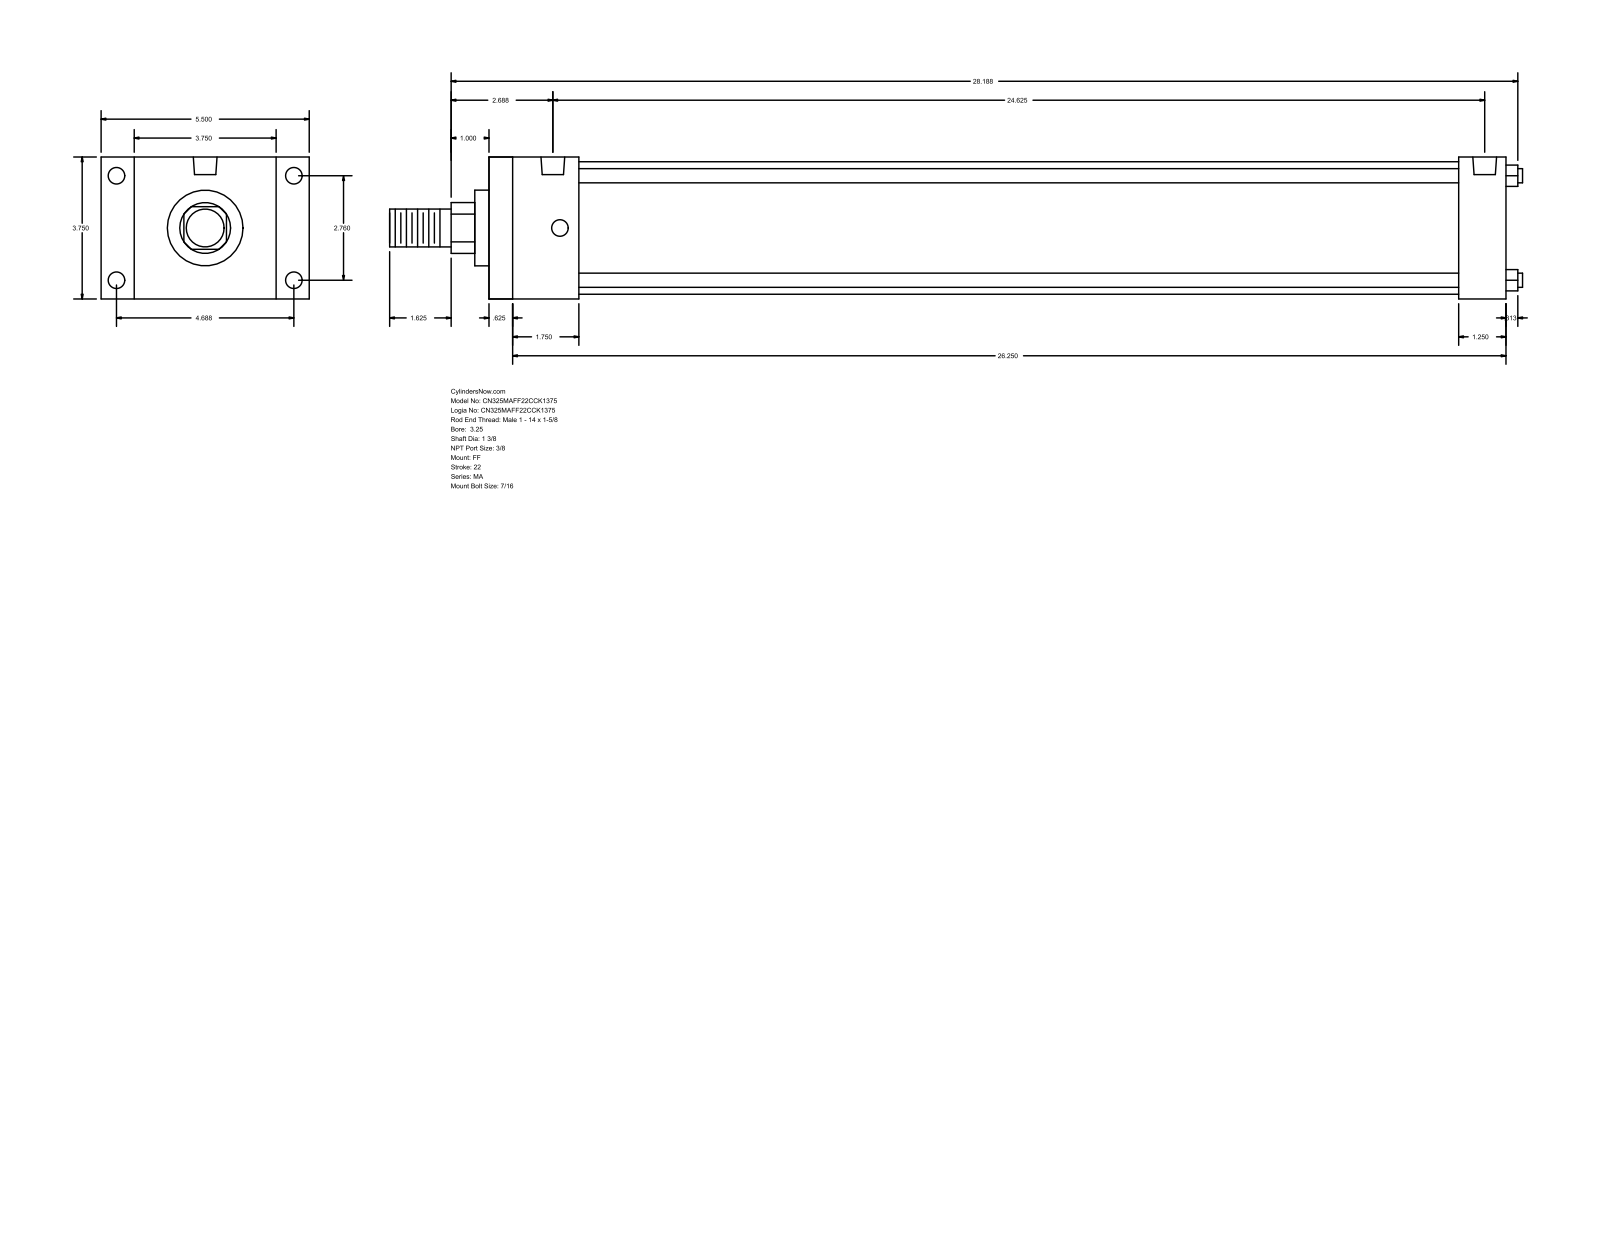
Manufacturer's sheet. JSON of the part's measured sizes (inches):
{"part_name": "MA_FF__0325_1.375", "step_written_by": "GSSL Pune (CONFIG_CONTROL_DESIGN)", "units": "inches", "bodies": {"solids": 0, "faces": 92, "planar": 64, "cylindrical": 28, "other": 0}, "overall_size": [29.937, 5.5, 3.75], "round_holes": [[0.437, 8], [0.627, 2]], "round_bosses_or_shafts": [[0.375, 4], [3.5, 1], [2, 1], [1.375, 1], [1, 1]], "partial_cylinders_radius": [[0.672, 1]], "face_to_face_distances": [3.75, 26.875, 0.625, 26.25, 0.875, 4.625, 2.375, 25.625, 1.75, 25], "hole_center_spacings": [2.76, 4.687, 5.439, 24.25, 0.187, 0.188, 24.437, 24.438]}
